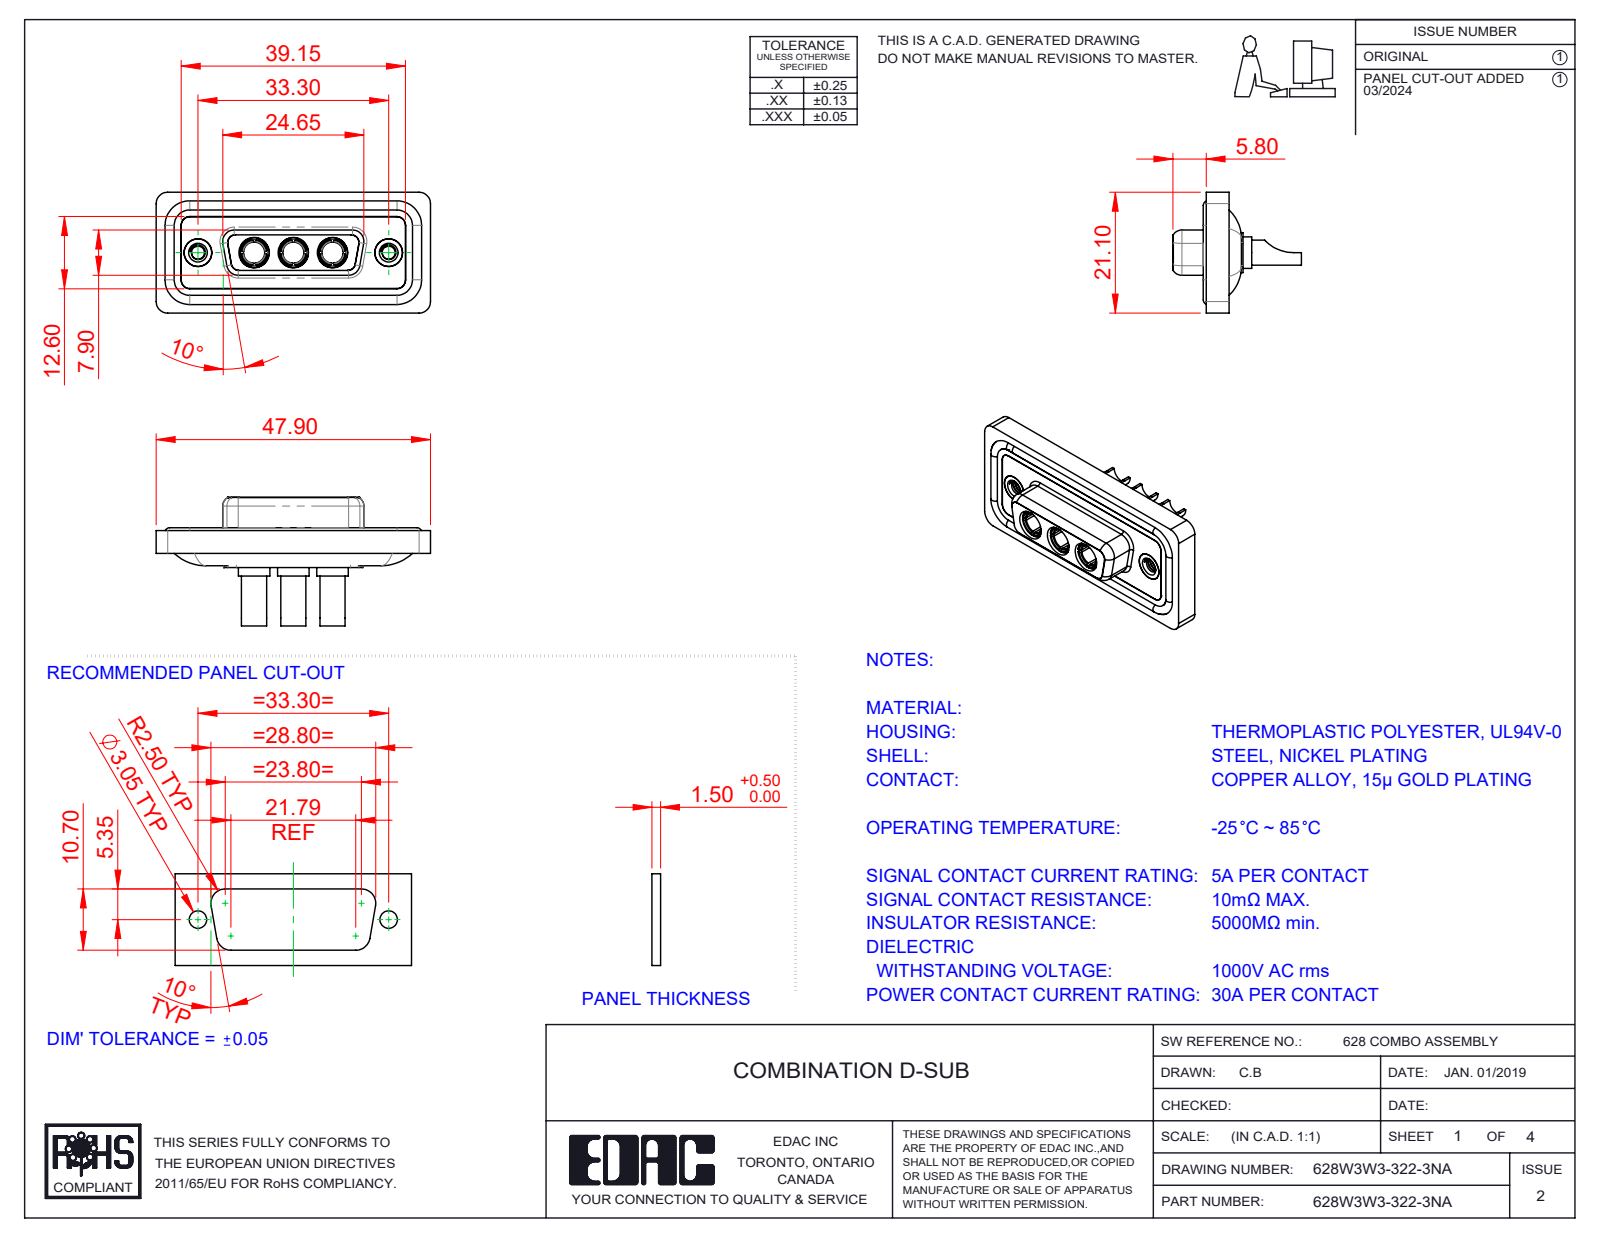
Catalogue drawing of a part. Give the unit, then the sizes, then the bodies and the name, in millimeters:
Units: millimetres
Overall size (bounding box): 47.9 × 22.45 × 21.1
Round holes (diameter × count): ⌀4.85 ×5, ⌀3.5 ×3, ⌀3.7 ×3, ⌀5.3 ×3, ⌀2.26 ×2, ⌀4 ×2, ⌀4.05 ×2, ⌀5 ×2
Round bosses / shafts (diameter × count): ⌀1.6 ×4, ⌀5.5 ×3, ⌀5.2 ×3, ⌀4.96 ×3, ⌀4.75 ×3, ⌀4.4 ×3, ⌀3.75 ×3, ⌀4.95 ×2
Partial cylindrical surfaces — rounded edges, fillets, slot ends (radius × count): R1.5 ×22, R2 ×20, R1.35 ×12, R1.6 ×8, R0.25 ×4, R0.5 ×4, R0.6 ×4, R0.65 ×4
Main face-to-face distances: 0.4, 1.8, 1.6, 0.5, 7.45, 1.1, 2.9, 5.65, 7.05, 6.6
Hole centre spacings: 6.85, 9.8, 16.65, 23.5, 13.7, 33.3
Volume: 6 100 mm³ · Surface area: 10 059 mm²
Bodies: 13 solids, 624 faces (201 planar, 268 cylindrical, 155 other)
Part name (STEP PRODUCT): 628Combo Waterproof Housing_15 Contacts; 628W3W3-322-3NA; 628Combo Shell Rear_15 Contacts; 628Combo Shell Front_15 Contacts (+3 more)
STEP written by: SolidWorks 2023 (CONFIG_CONTROL_DESIGN)
